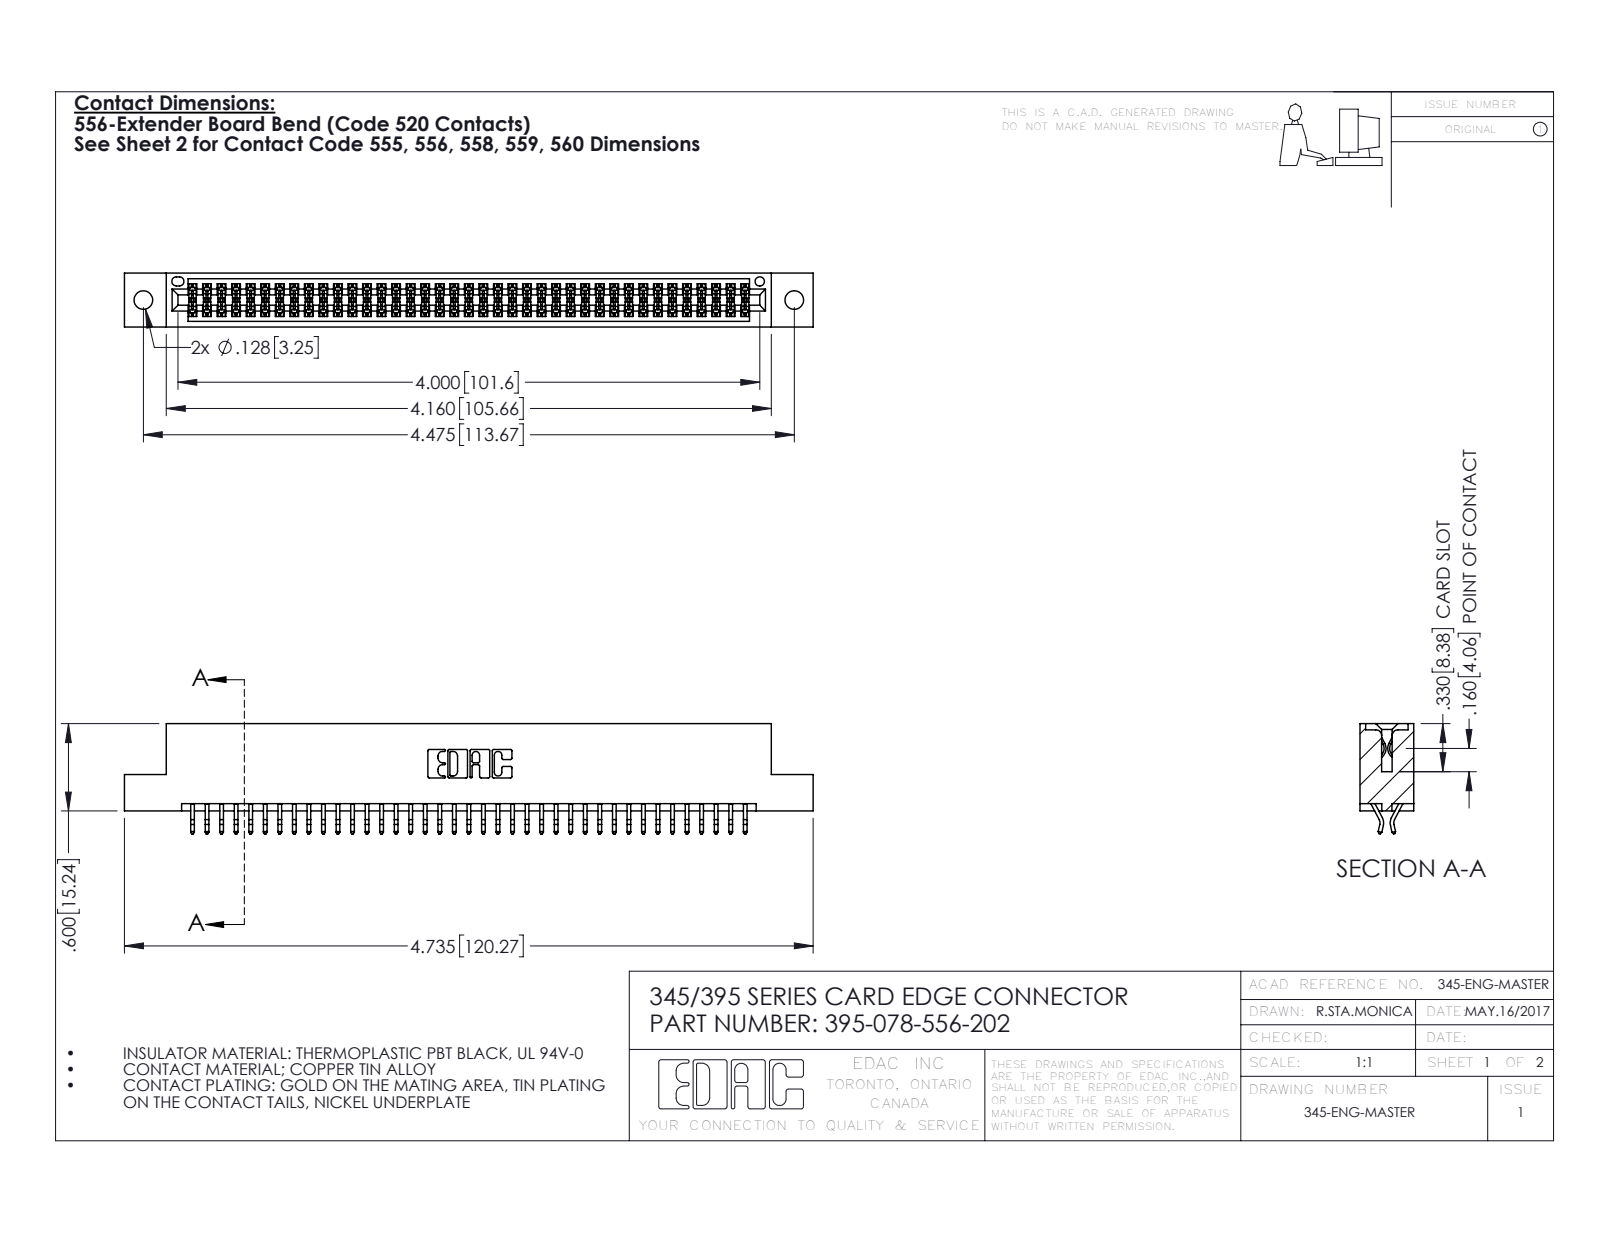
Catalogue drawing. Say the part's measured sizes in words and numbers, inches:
The part is named "345 Part_Flush Mounting Lugs - 0.128 Dia; 345-292-001_556 Tail; 395-078-556-202". Its 3-D file was written by "SolidWorks 2016 (CONFIG_CONTROL_DESIGN)". It is 79 solids with 4494 faces: 2966 planar, 1528 cylindrical and 0 other. Overall it measures 4.735 by 0.757 by 0.37 inches. Its volume is 0.709 cubic inches and its surface area 25.99 square inches. Round holes: 2 of diameter 0.128, 1 of diameter 0.064. Partial cylindrical surfaces (rounded edges, fillets, slot ends): 117 of radius 0.006, 22 of radius 0.01, 6 of radius 0.007, 6 of radius 0.031, 3 of radius 0.026, 2 of radius 0.01, 2 of radius 0.014, 2 of radius 0.019. The main face-to-face distances are 0.298, 0.072, 0.37, 0.2, 0.025, 0.098, 0.272, 0.225, 0.175, 0.149. The hole center spacings are 0.27, 4.239, 4.475.
